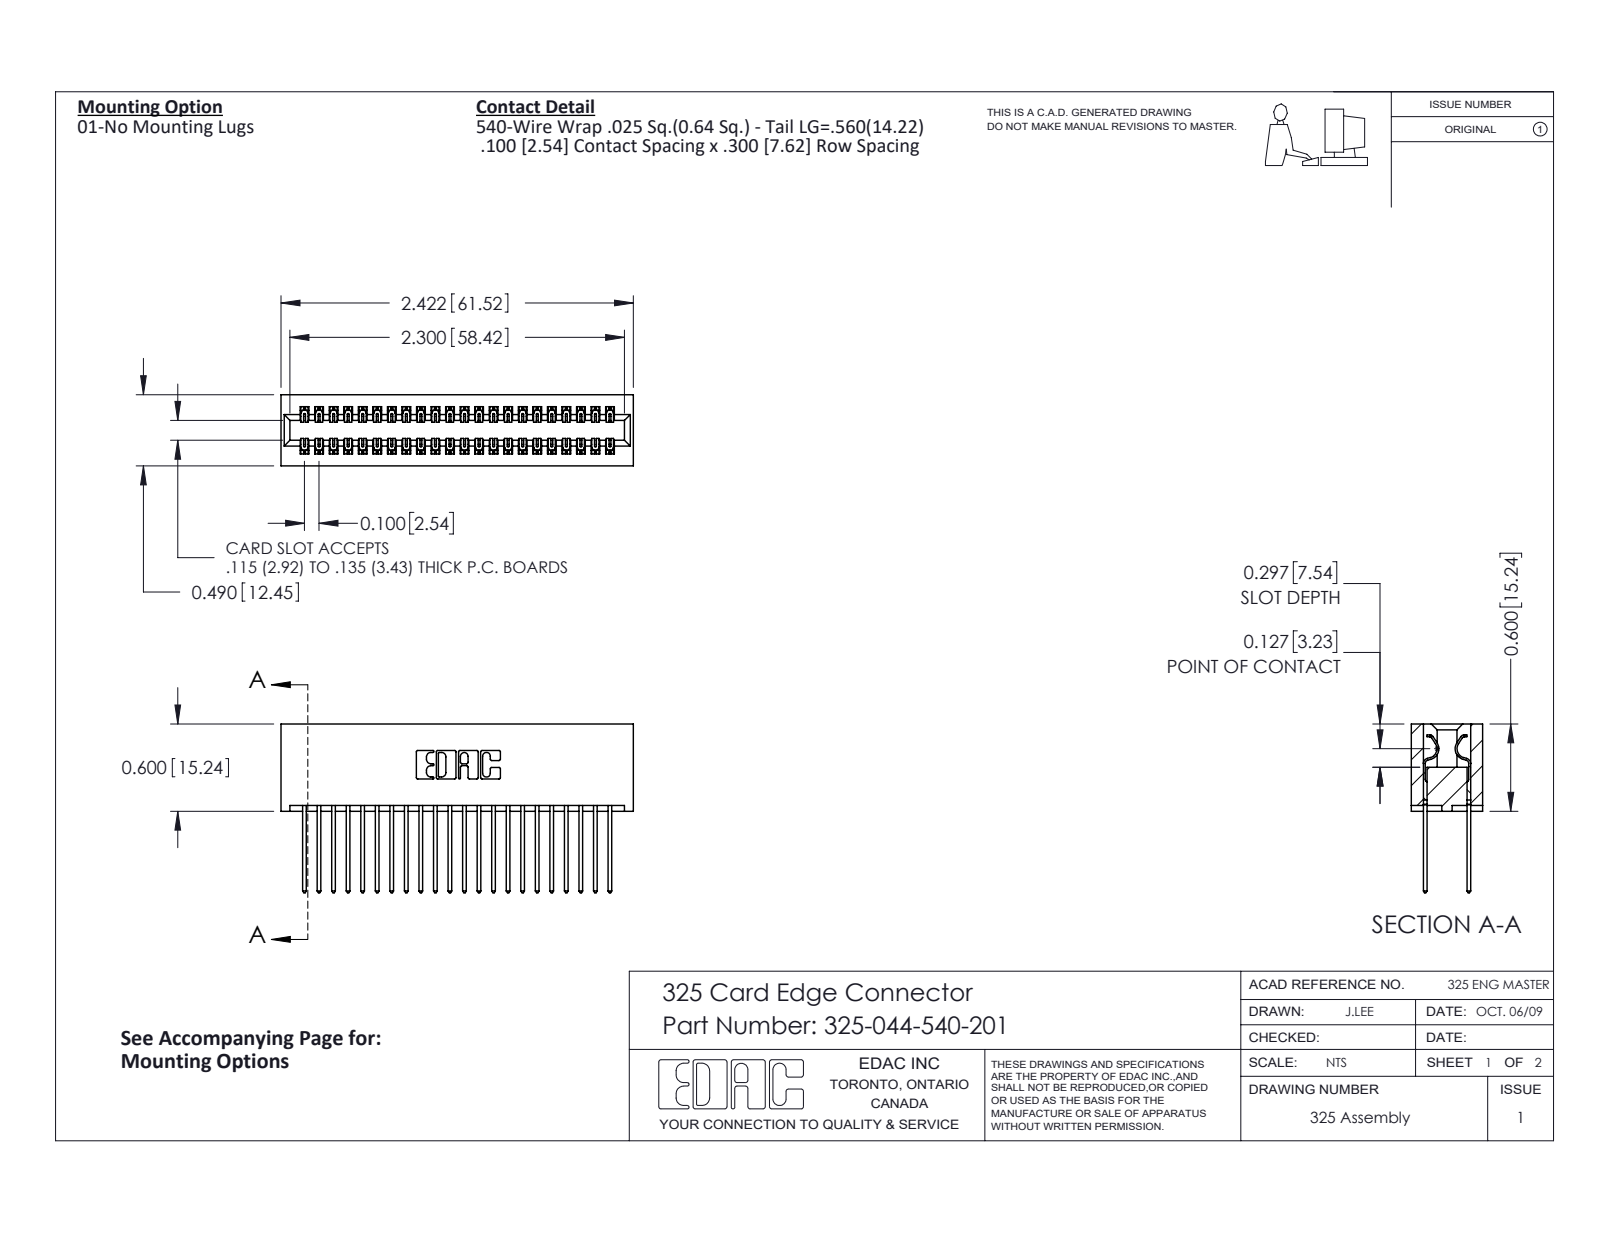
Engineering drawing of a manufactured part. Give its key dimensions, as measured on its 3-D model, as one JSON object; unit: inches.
{"part_name": "325 Part_Lugless; 325-292-001_325-293-140; 325-044-540-201", "step_written_by": "SolidWorks 2016 (CONFIG_CONTROL_DESIGN)", "units": "inches", "bodies": {"solids": 45, "faces": 2394, "planar": 1650, "cylindrical": 744, "other": 0}, "overall_size": [2.422, 1.16, 0.49], "volume_in3": 0.521, "surface_area_in2": 17.53, "partial_cylinders_radius": [[0.006, 66], [0.01, 44], [0.01, 22], [0.007, 6], [0.031, 6], [0.026, 3], [0.014, 2], [0.022, 2]], "face_to_face_distances": [0.083, 0.407, 0.3, 0.107, 0.383, 0.025, 0.325, 0.49, 0.275, 0.1]}
